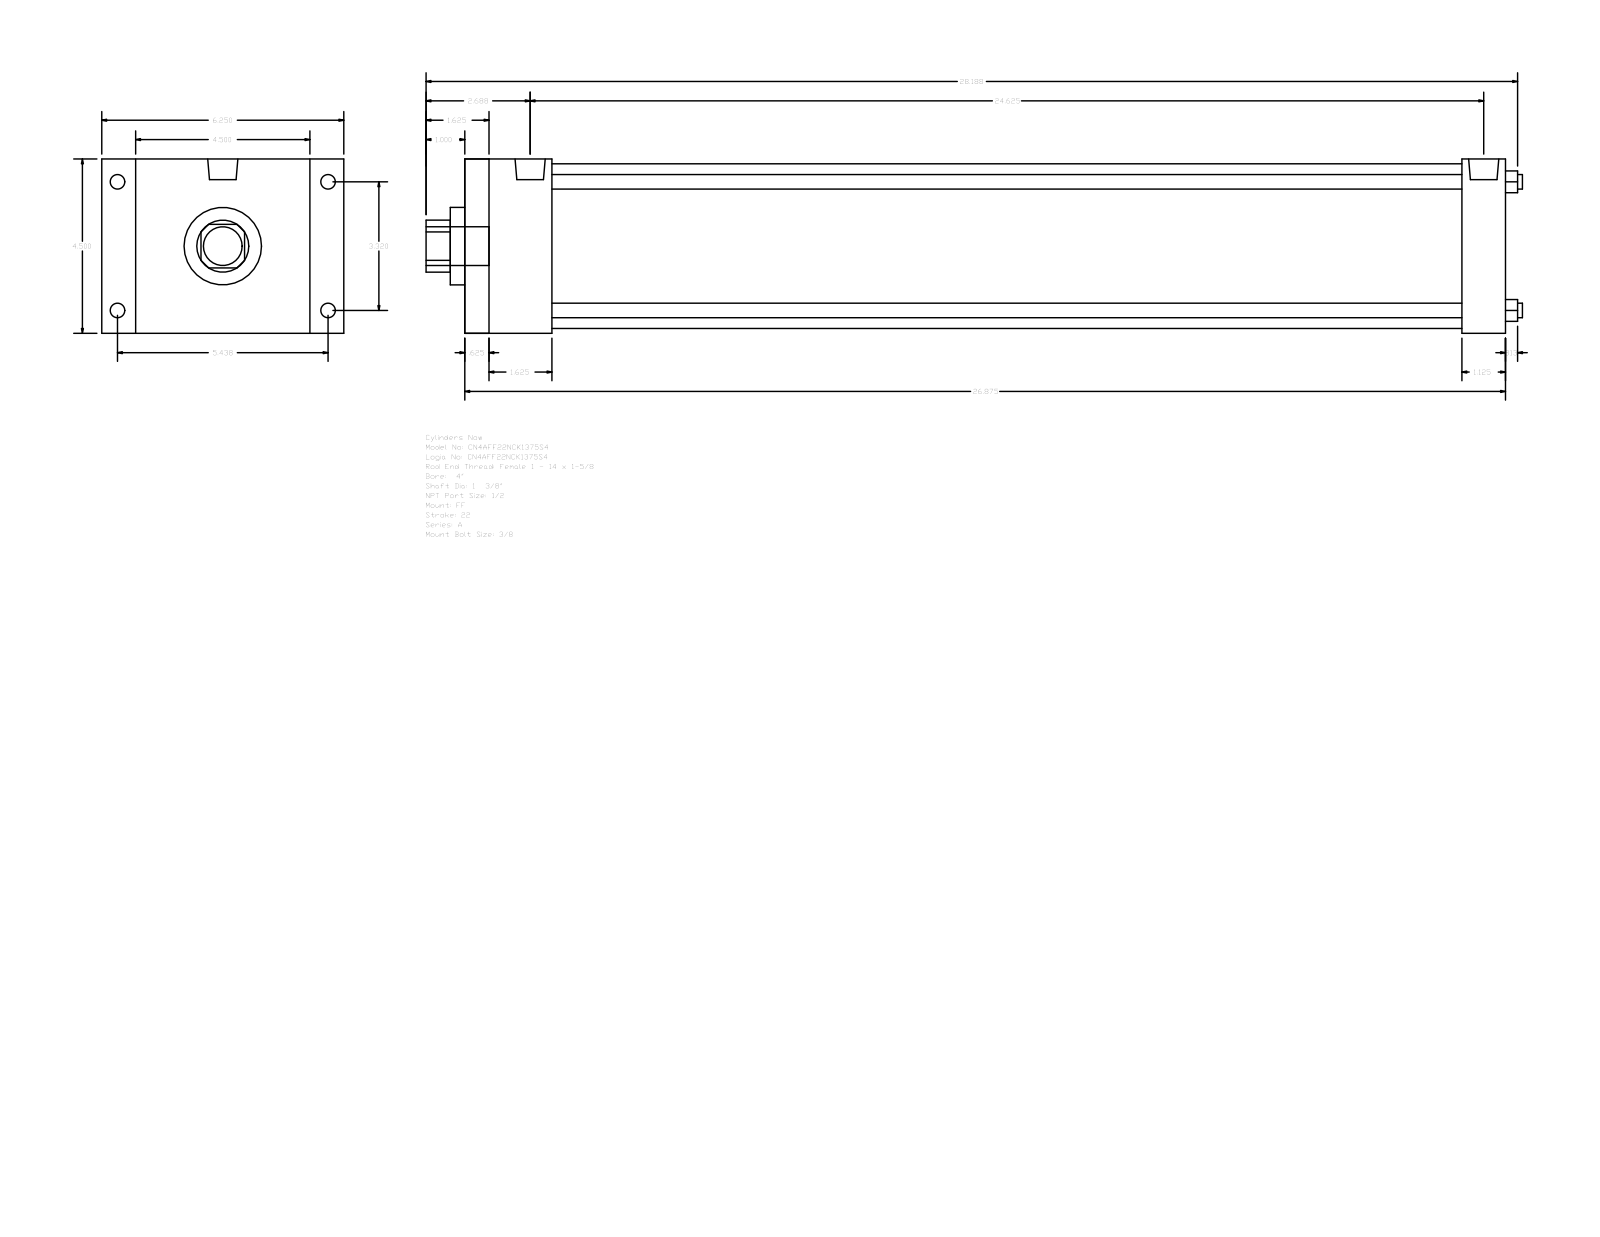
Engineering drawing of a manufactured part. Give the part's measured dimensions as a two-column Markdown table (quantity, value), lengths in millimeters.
| quantity | value |
| --- | --- |
| part name | A_FF__0400_1.375 |
| STEP written by | GSSL Pune (CONFIG_CONTROL_DESIGN) |
| units | millimeters |
| bodies | 0 solids, 92 faces (64 planar, 28 cylindrical, 0 other) |
| overall size | 719.14 × 158.75 × 114.3 |
| round holes (diameter × count) | 9.53 × 4, 34.92 × 1, 50.8 × 1, 107.95 × 1 |
| round bosses / shafts (diameter × count) | 9.53 × 4, 8.73 × 4, 19.77 × 2, 25.4 × 1 |
| partial cylindrical surfaces (radius × count) | 17.06 × 1 |
| main face-to-face distances | 114.3, 682.62, 666.75, 15.87, 28.57, 22.23, 136.53, 654.05, 638.18, 57.15 |
| hole center spacings | 59.62, 84.32, 119.25 |
